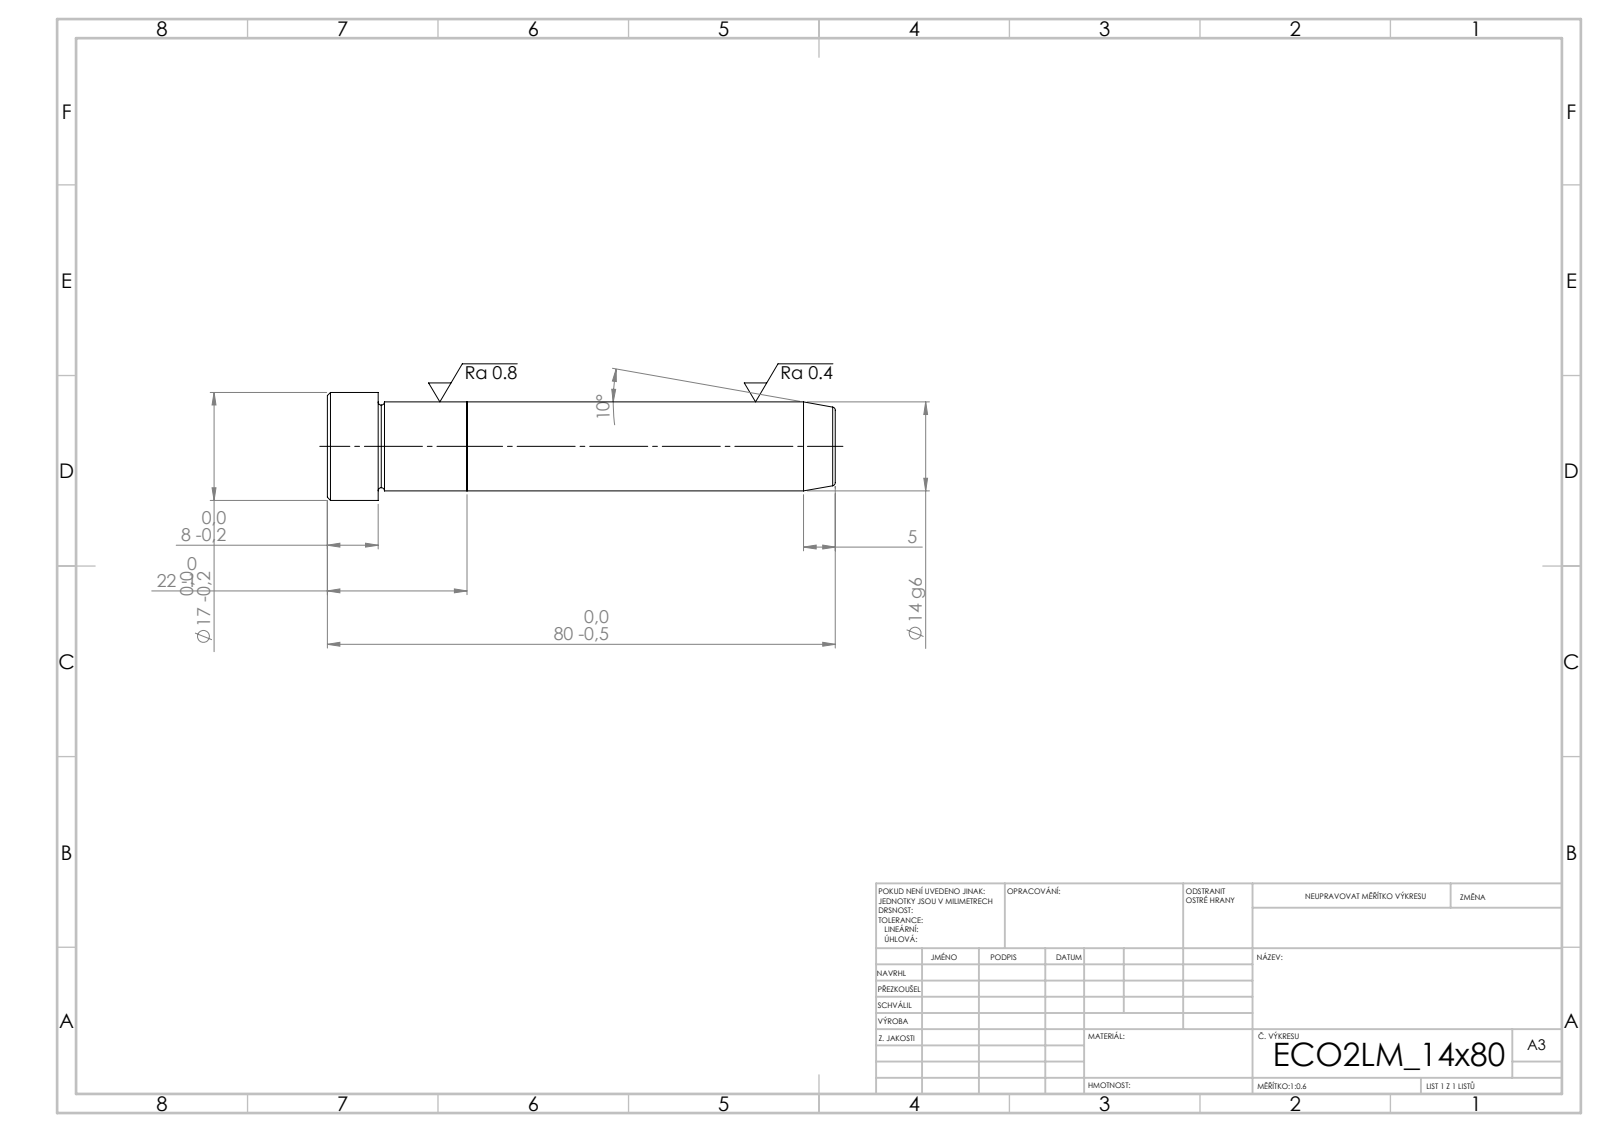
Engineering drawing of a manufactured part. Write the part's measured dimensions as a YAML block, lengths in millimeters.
step_written_by: "SolidWorks 2019 (CONFIG_CONTROL_DESIGN)"
units: millimeters
bodies: {solids: 2, faces: 21, planar: 5, cylindrical: 6, other: 10}
overall_size: [80, 17, 17]
volume: 12782
surface_area: 4309
round_bosses_or_shafts:
  - {diameter: 17, count: 1}
  - {diameter: 14, count: 1}
face_to_face_distances: [22, 58, 80, 72, 14, 8]
